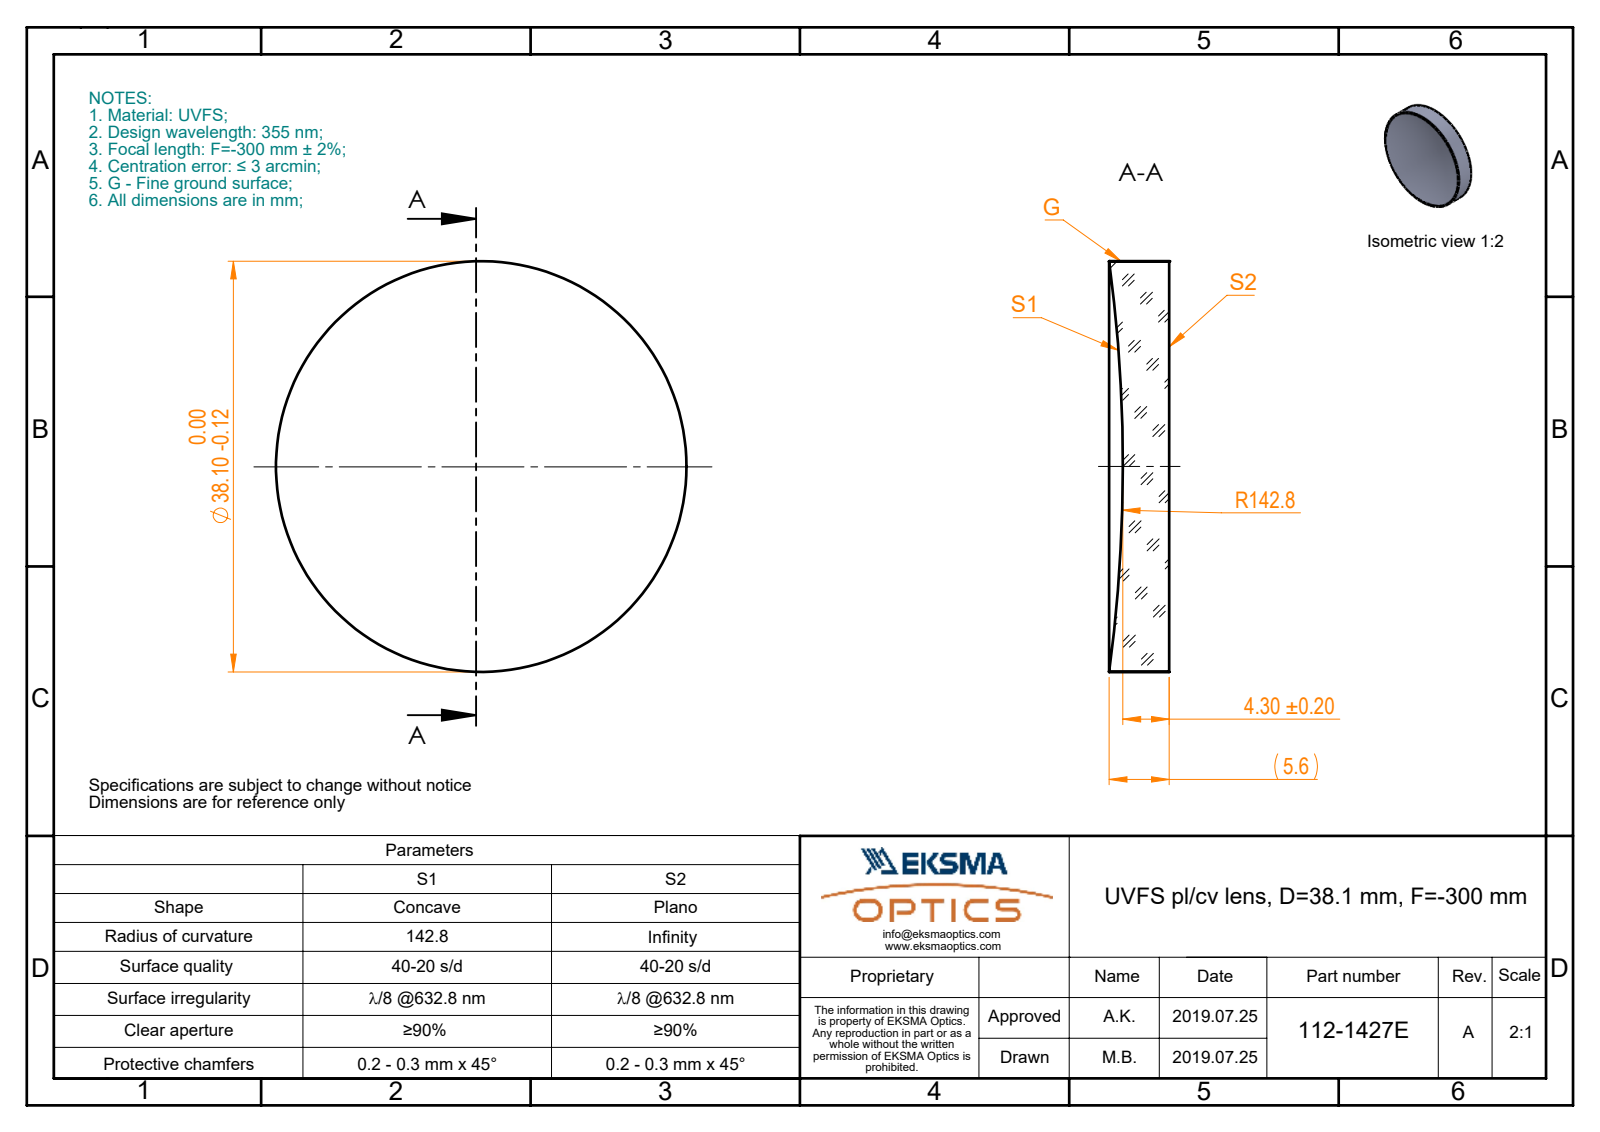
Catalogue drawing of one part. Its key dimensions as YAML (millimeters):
part_name: "112-1427E UVFS pl-cv 38.1 F-300"
step_written_by: "SolidWorks 2017 (CONFIG_CONTROL_DESIGN)"
units: millimeters
bodies: {solids: 1, faces: 5, planar: 1, cylindrical: 2, other: 2}
overall_size: [38.1, 38.1, 5.58]
volume: 5629
surface_area: 2953
round_bosses_or_shafts:
  - {diameter: 38.1, count: 1}
